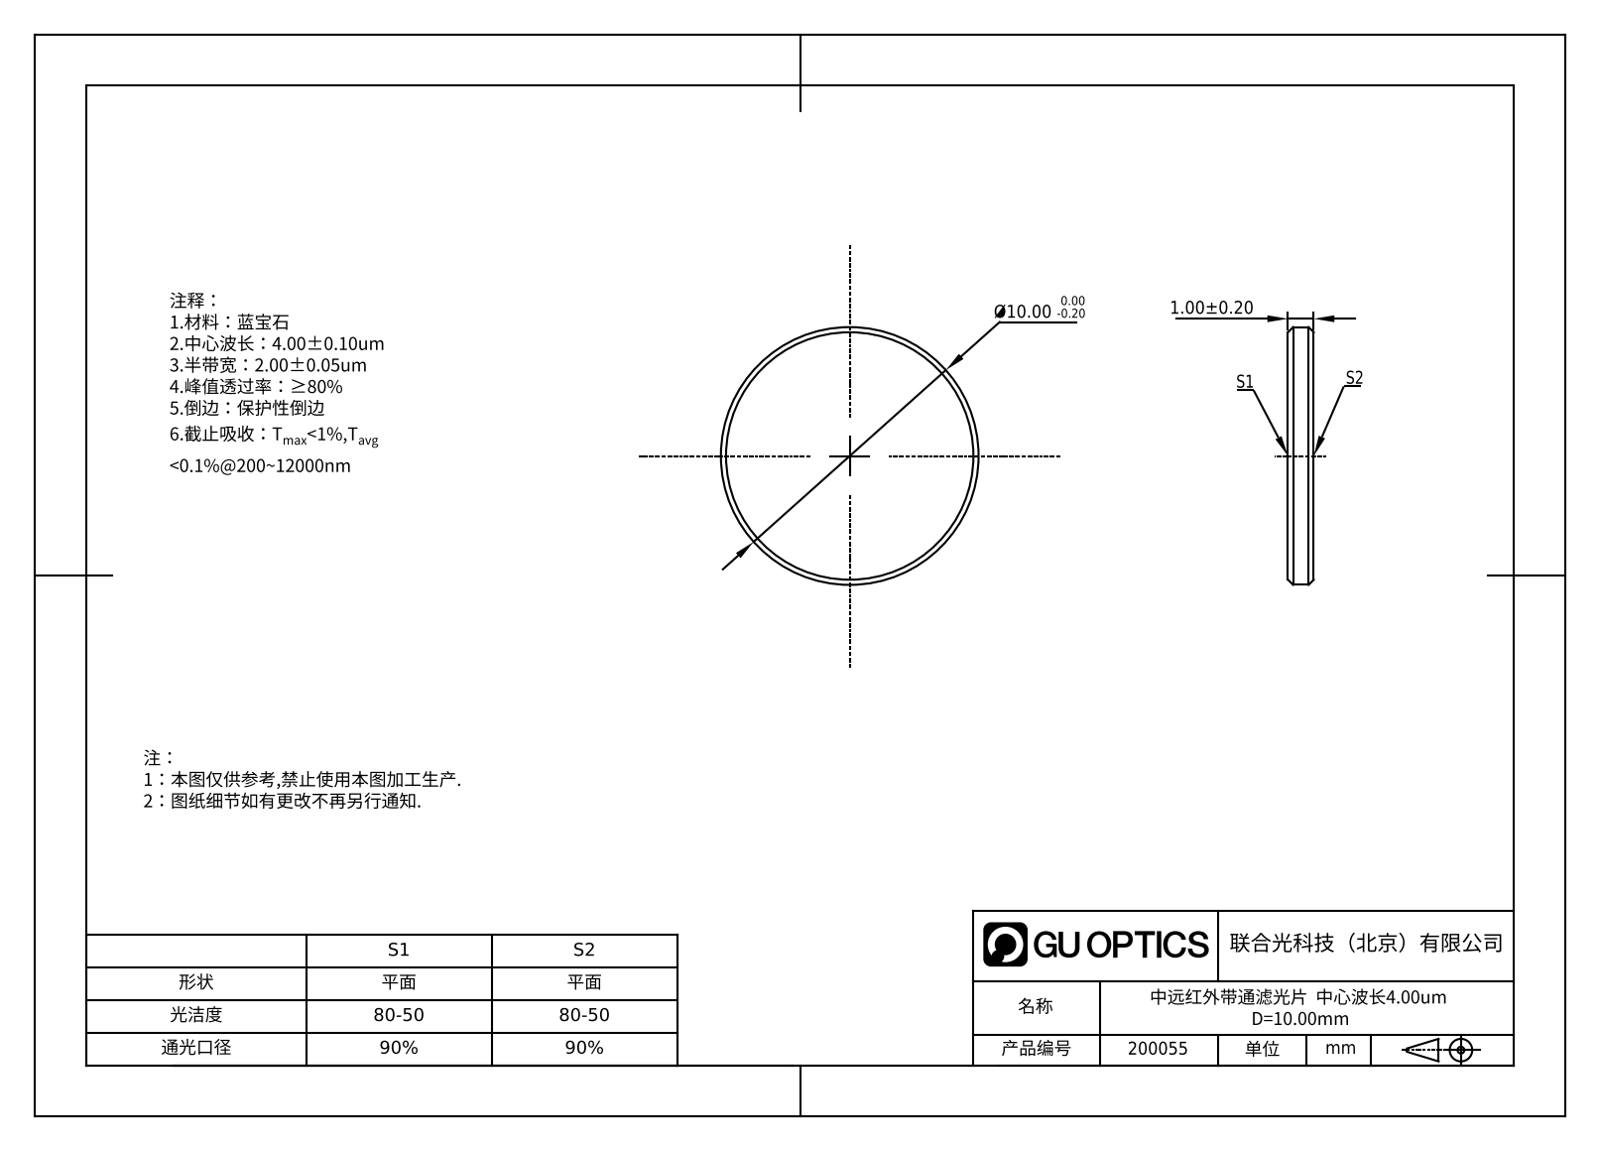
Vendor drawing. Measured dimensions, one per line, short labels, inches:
name: GNIF-2000-4000-D10
written by: SolidWorks 2022 (AUTOMOTIVE_DESIGN)
unit: in
bodies: 1 solid, 8 faces (2 planar, 2 cylindrical, 4 other)
size: 0.394 × 0.394 × 0.039
volume: 0.005 in³; area: 0.281 in²
bosses: 1× ⌀0.394
face distances: 0.039
